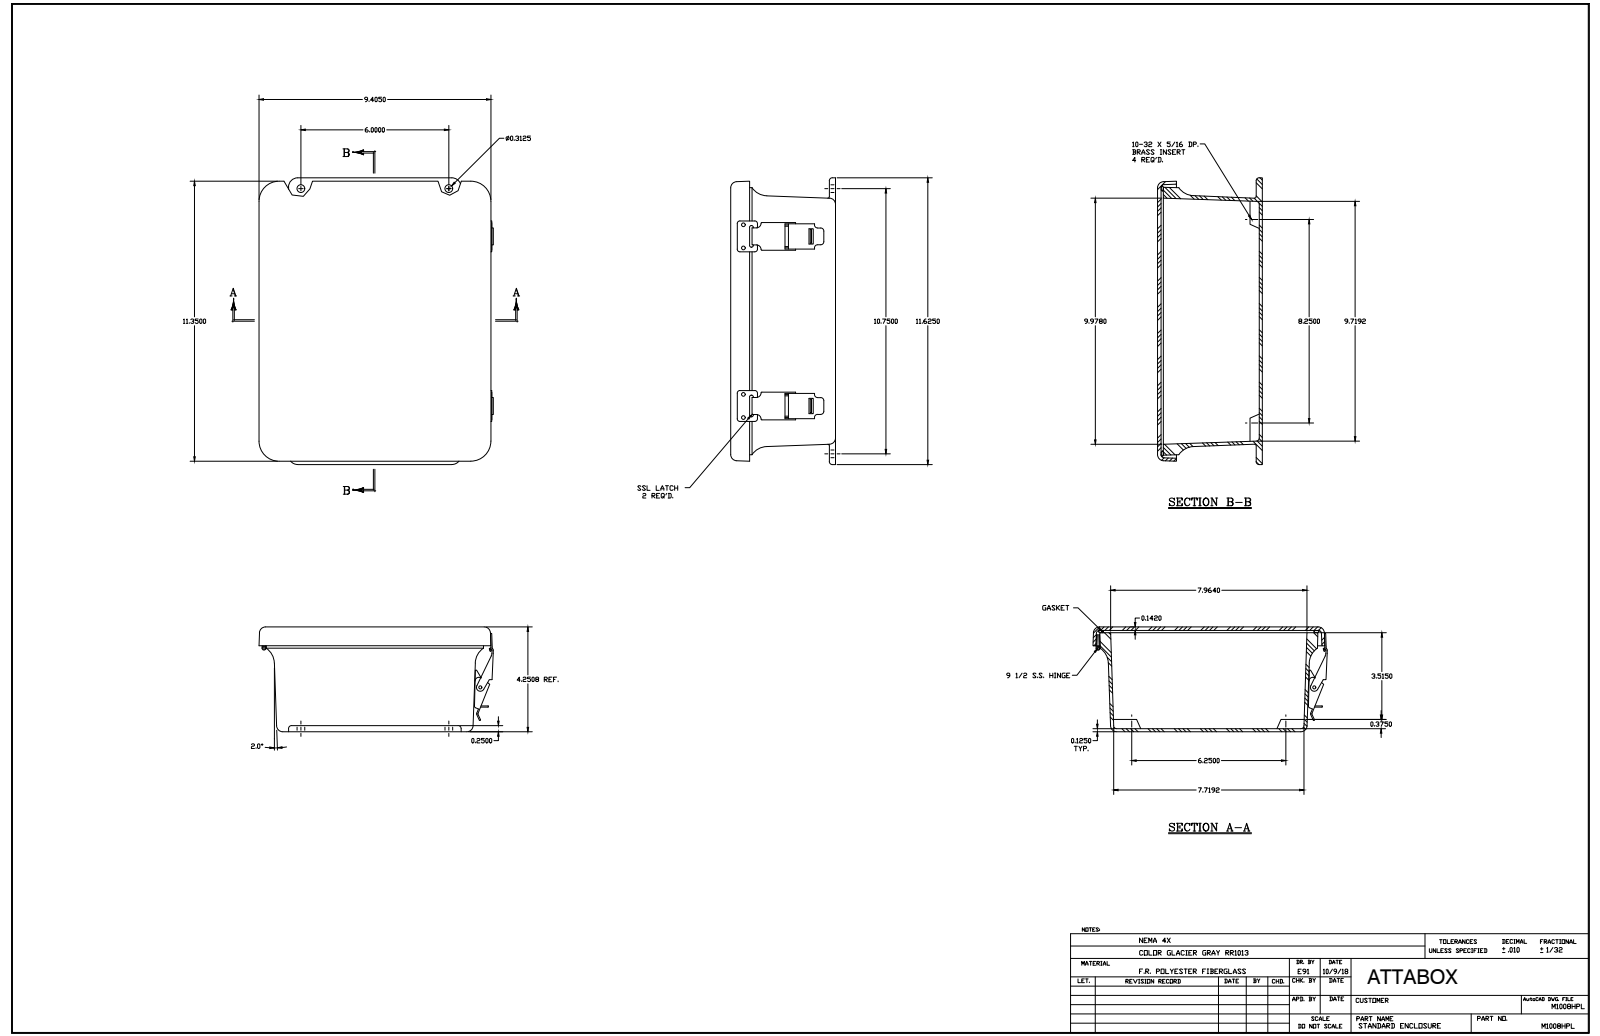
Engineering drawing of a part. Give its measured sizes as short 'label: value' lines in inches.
name: M1008HPL
written by: SolidWorks 2018 (AUTOMOTIVE_DESIGN)
unit: in
bodies: 38 solids, 939 faces (399 planar, 393 cylindrical, 147 other)
size: 11.625 × 9.533 × 4.234
volume: 61.27 in³; area: 837.7 in²
holes: 20× ⌀0.14, 8× ⌀0.104, 8× ⌀0.131, 5× ⌀0.152, 4× ⌀0.13, 4× ⌀0.156, 4× ⌀0.218, 2× ⌀0.135, 2× ⌀0.375, 1× ⌀0.085, 1× ⌀0.085
bosses: 12× ⌀0.125, 8× ⌀0.25, 4× ⌀0.27, 4× ⌀0.125, 1× ⌀0.3, 1× ⌀0.17, 1× ⌀0.155, 1× ⌀0.135
rounds: 20× R0.015, 20× R0.031, 20× R0.125, 16× R0.045, 12× R0.03, 8× R0.023, 8× R0.25, 6× R0.06
face distances: 0.142, 4.093, 4.235, 0.125, 3.968, 4.11, 0.12, 3.89, 4.015, 0.078
hole spacings: 7, 0.75, 7.04, 0.937, 6, 3, 0.25, 1.468
